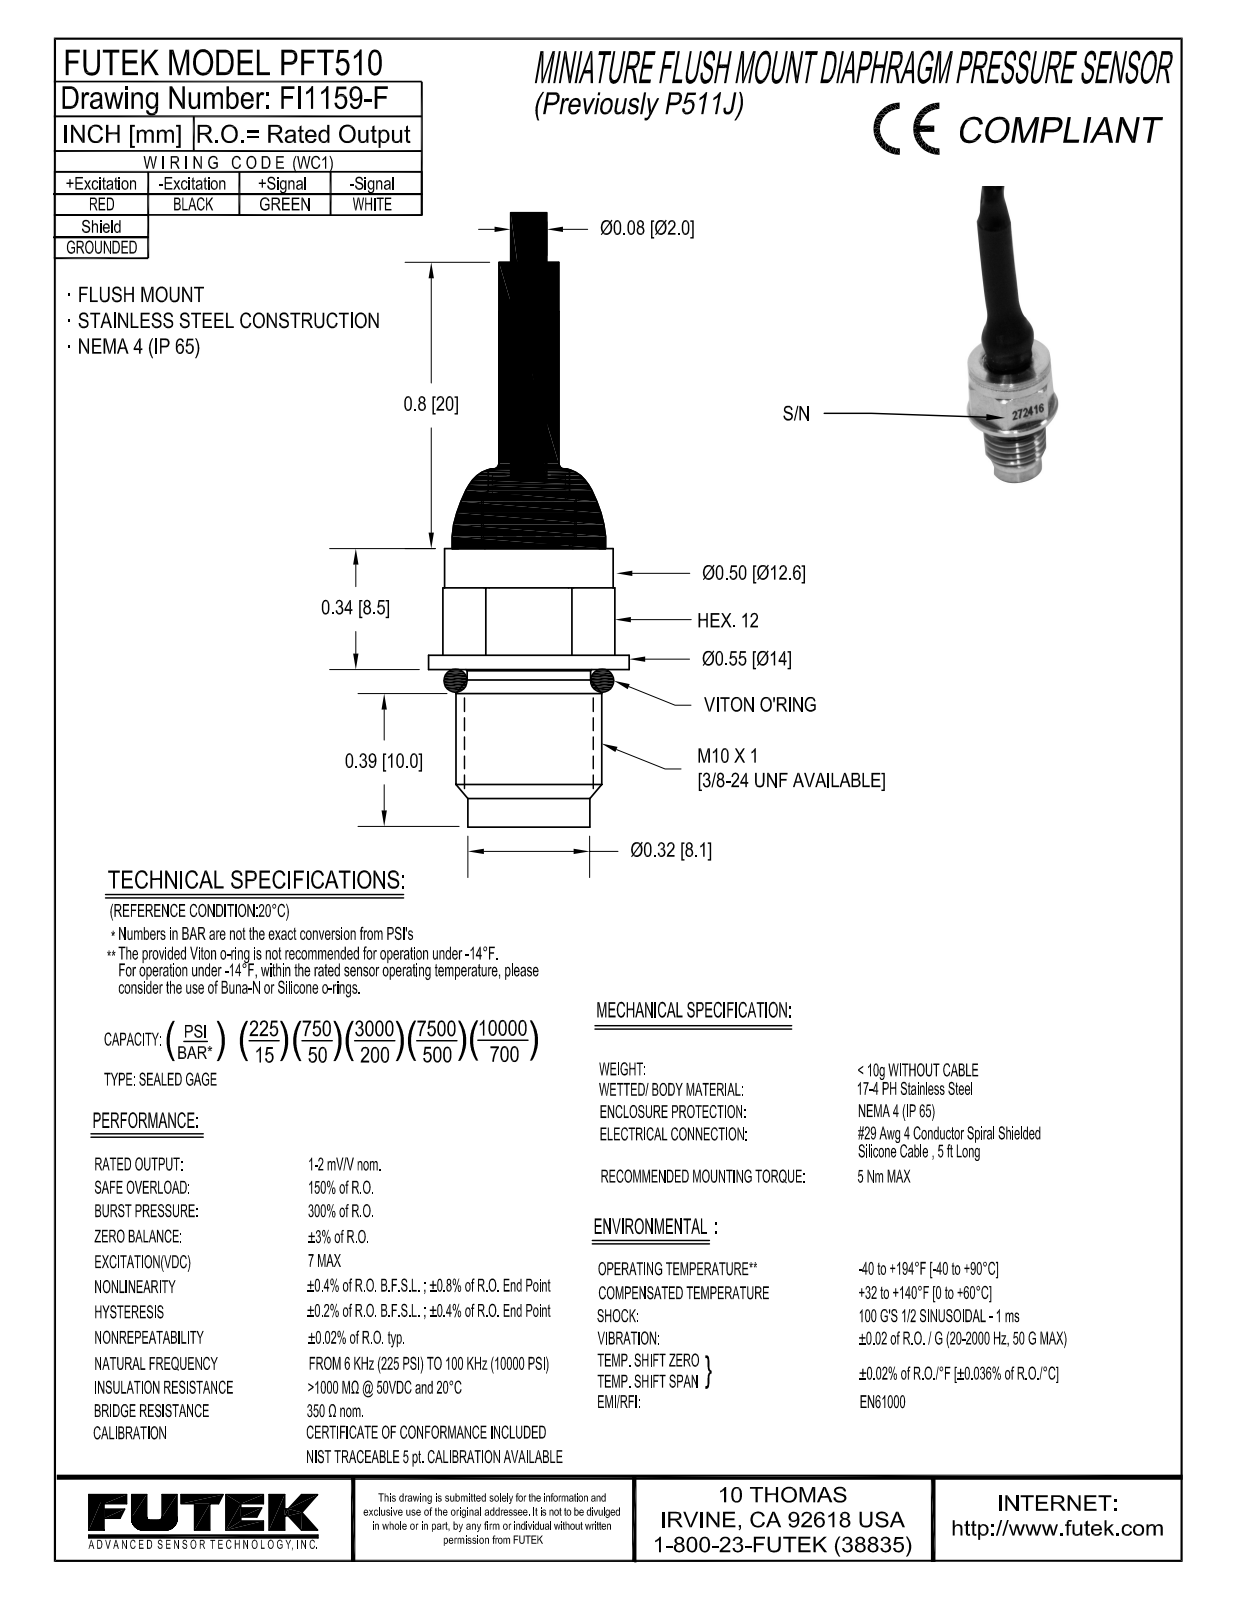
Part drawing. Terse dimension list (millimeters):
name: PFT510 (3-8-24 THREAD)
written by: Mechanical Desktop 2008 (CONFIG_CONTROL_DESIGN)
unit: mm
bodies: 2 solids, 68 faces (22 planar, 26 cylindrical, 20 other)
size: 53.9 × 14 × 14
volume: 2 790 mm³; area: 2 105 mm²
bosses: 1× ⌀14, 1× ⌀12.6, 1× ⌀11.2, 1× ⌀10.2, 1× ⌀8.6, 1× ⌀8.5, 1× ⌀6.5, 1× ⌀6.4
face distances: 5.7, 2.3, 2.7, 8.5, 0.5, 8, 7.4, 7, 4.7, 1
